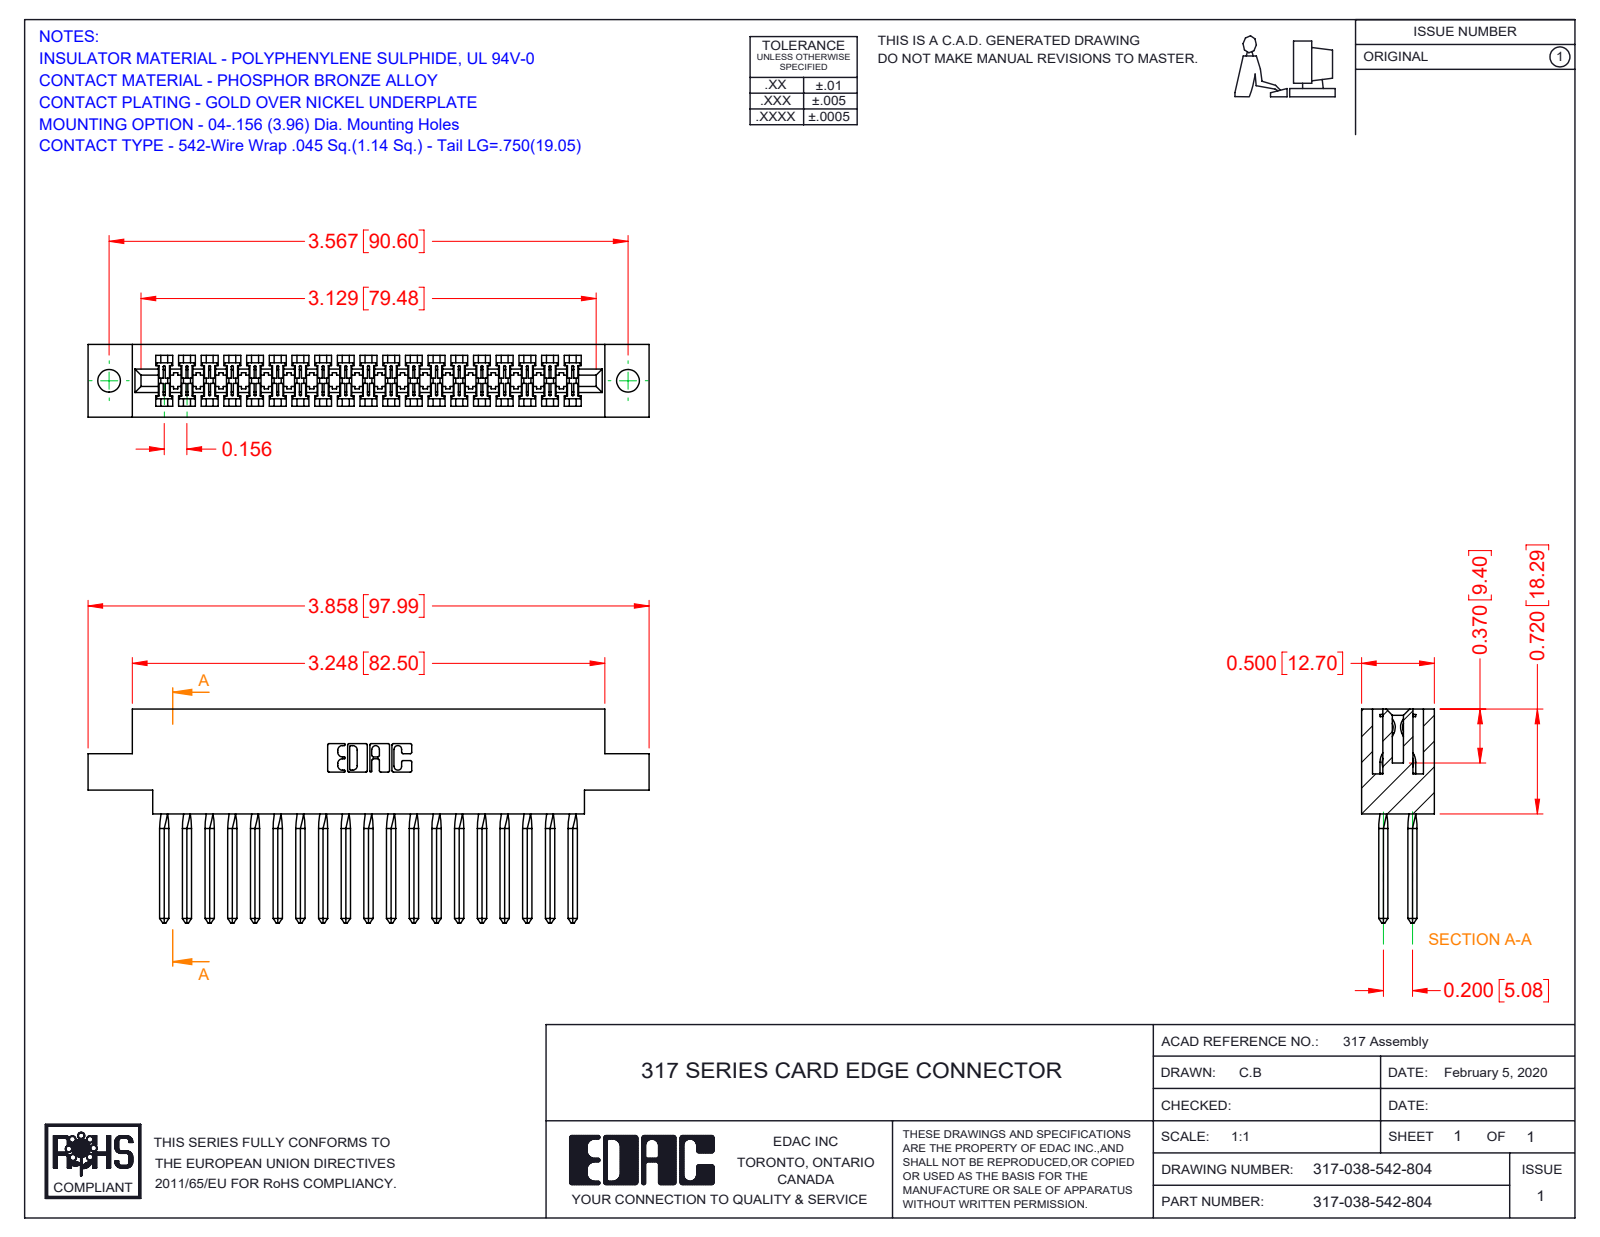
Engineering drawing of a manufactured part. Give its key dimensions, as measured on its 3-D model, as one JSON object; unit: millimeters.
{"part_name": "317-038-542-804; 317-290-003_542; 317 Part_.156 Dia - TH", "step_written_by": "SolidWorks 2016 (CONFIG_CONTROL_DESIGN)", "units": "millimeters", "bodies": {"solids": 39, "faces": 2268, "planar": 1806, "cylindrical": 310, "other": 152}, "overall_size": [98, 37.3, 12.7], "volume_mm3": 15200, "surface_area_mm2": 20260, "round_holes": [[4, 2]], "partial_cylinders_radius": [[0.2, 76], [0.3, 22], [0.2, 6], [0.8, 6], [0.7, 3], [1.9, 2], [2.3, 2], [2.5, 2]], "face_to_face_distances": [12.7, 1.9, 10.8, 2.8, 8.9, 5.1, 2.9, 3.5, 18.3, 1.2], "hole_center_spacings": [90.6]}
